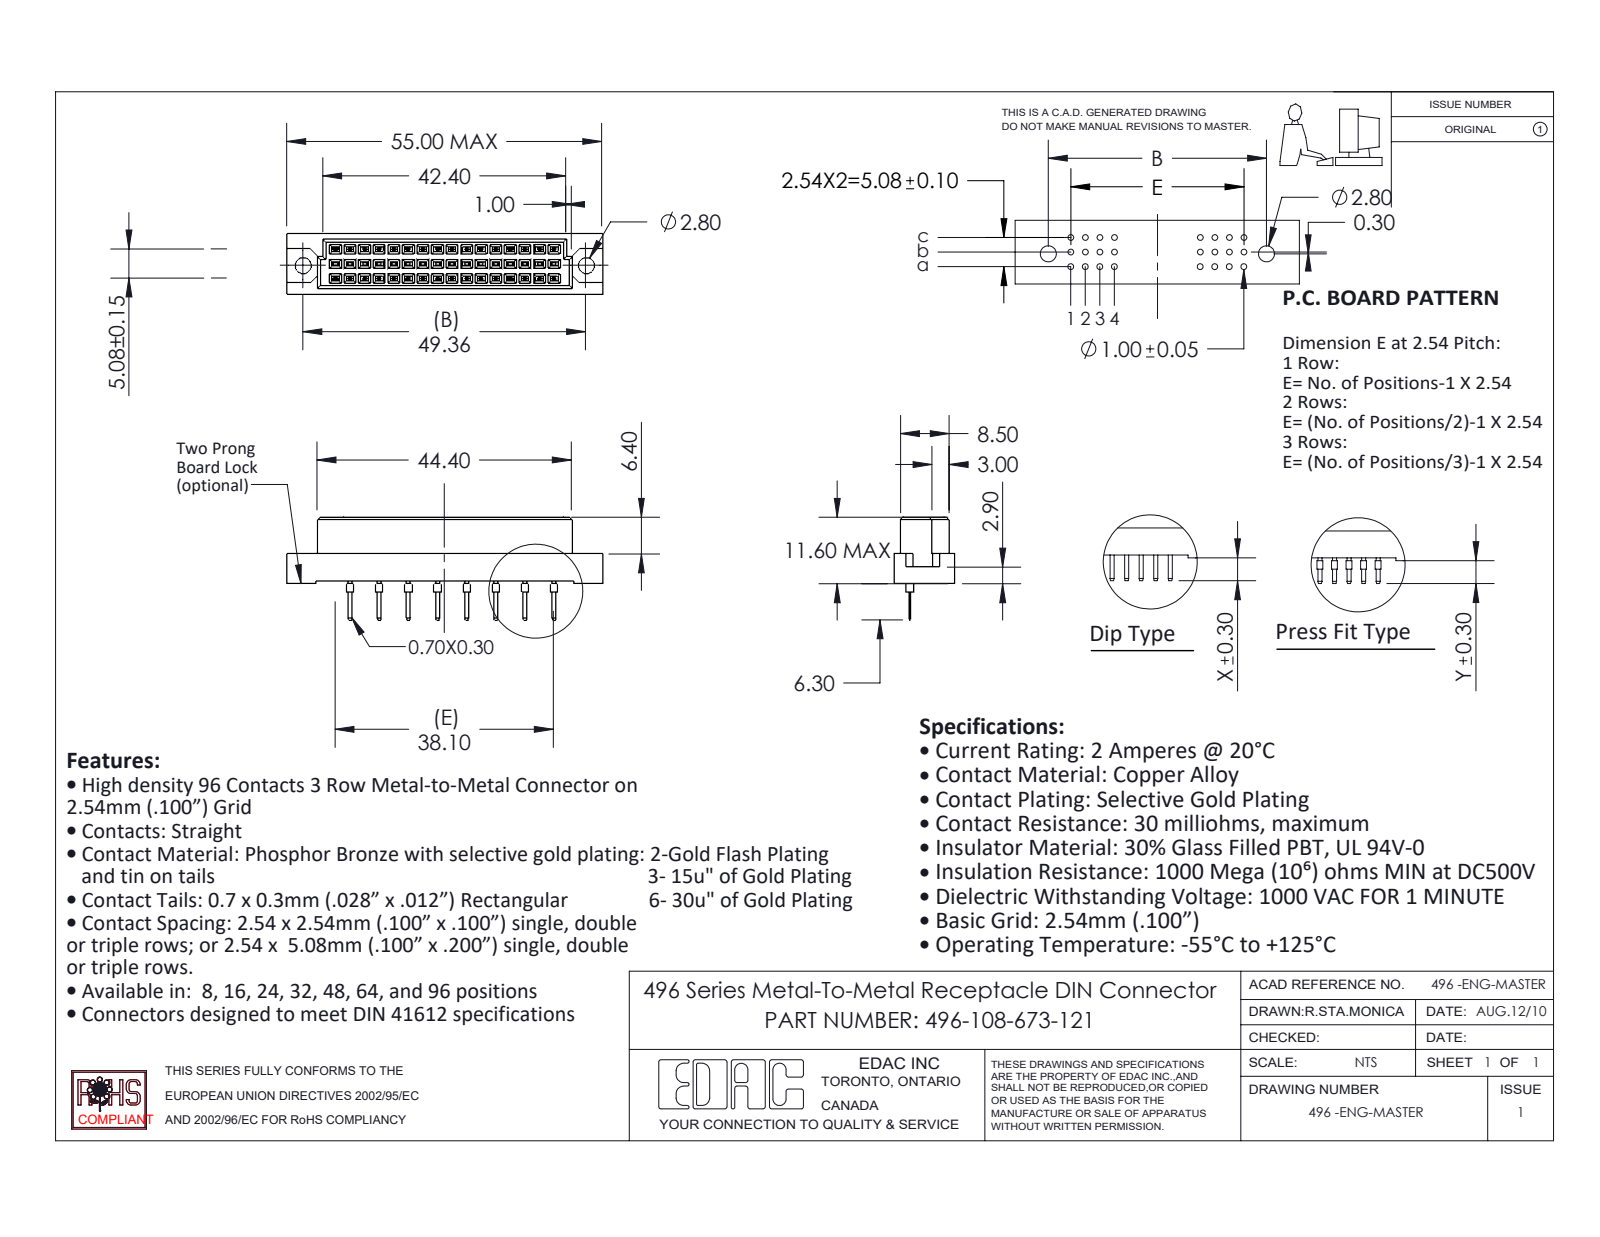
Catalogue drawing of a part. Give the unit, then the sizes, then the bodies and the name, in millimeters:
Units: millimetres
Overall size (bounding box): 55 × 17.9 × 10.6
Round holes (diameter × count): ⌀2.8 ×2
Round bosses / shafts (diameter × count): ⌀1 ×8
Main face-to-face distances: 2.54, 5.08, 1.05, 9.55, 0.81, 10.6, 3.35, 1.73, 8.5, 0.56
Hole centre spacings: 49.36
Volume: 4 615 mm³ · Surface area: 4 417 mm²
Bodies: 9 solids, 810 faces (790 planar, 20 cylindrical, 0 other)
Part name (STEP PRODUCT): 496-290_73; 496-108-673-121; 496 Part_48
STEP written by: SolidWorks 2020 (CONFIG_CONTROL_DESIGN)
